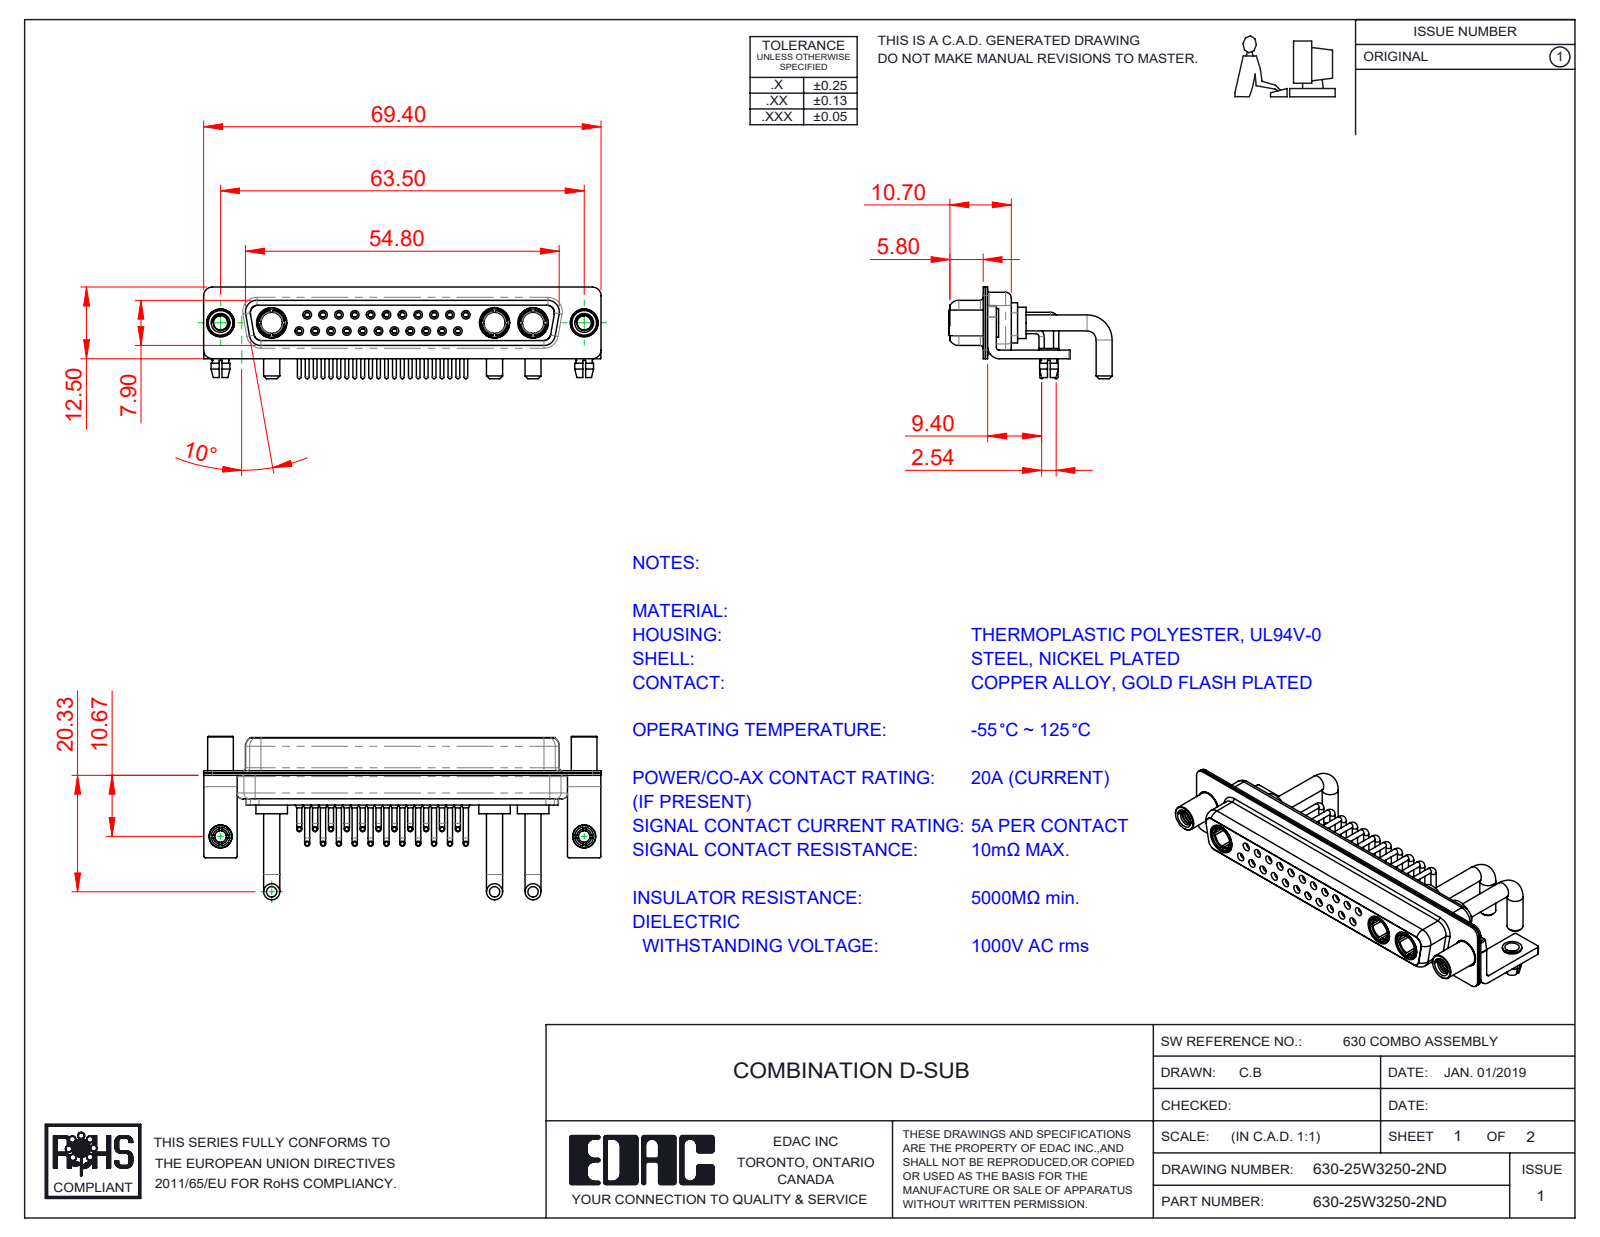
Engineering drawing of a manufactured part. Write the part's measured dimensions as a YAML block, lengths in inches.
part_name: "630Combo Shell Rear_37 Contacts; 630Combo Stabilizer Bracket; 630Combo Board Lock; Power Socket_Ext 20A RA (+6 more)"
step_written_by: "SolidWorks 2020 (CONFIG_CONTROL_DESIGN)"
units: inches
bodies: {solids: 37, faces: 1869, planar: 554, cylindrical: 822, other: 493}
overall_size: [2.732, 1.123, 0.63]
volume: 0.38
surface_area: 21.76
round_holes:
  - {diameter: 0.079, count: 24}
  - {diameter: 0.035, count: 22}
  - {diameter: 0.043, count: 22}
  - {diameter: 0.059, count: 22}
  - {diameter: 0.063, count: 11}
  - {diameter: 0.067, count: 11}
  - {diameter: 0.191, count: 5}
  - {diameter: 0.098, count: 4}
  - {diameter: 0.146, count: 3}
  - {diameter: 0.209, count: 3}
  - {diameter: 0.126, count: 2}
  - {diameter: 0.157, count: 2}
round_bosses_or_shafts:
  - {diameter: 0.035, count: 23}
  - {diameter: 0.026, count: 22}
  - {diameter: 0.063, count: 12}
  - {diameter: 0.11, count: 6}
  - {diameter: 0.217, count: 3}
  - {diameter: 0.205, count: 3}
  - {diameter: 0.195, count: 3}
  - {diameter: 0.187, count: 3}
partial_cylinders:
  - {radius: 0.01, count: 16}
  - {radius: 0.059, count: 16}
  - {radius: 0.079, count: 13}
  - {radius: 0.053, count: 8}
  - {radius: 0.063, count: 8}
  - {radius: 0.02, count: 5}
  - {radius: 0.024, count: 4}
  - {radius: 0.026, count: 4}
face_to_face_distances: [0.016, 0.018, 0.055, 0.333, 0.071, 0.35, 0.244, 0.278, 0.031, 0.053]
hole_center_spacings: [0.124, 0.109, 0.218, 0.198, 0.327, 0.294, 0.436, 0.198]
